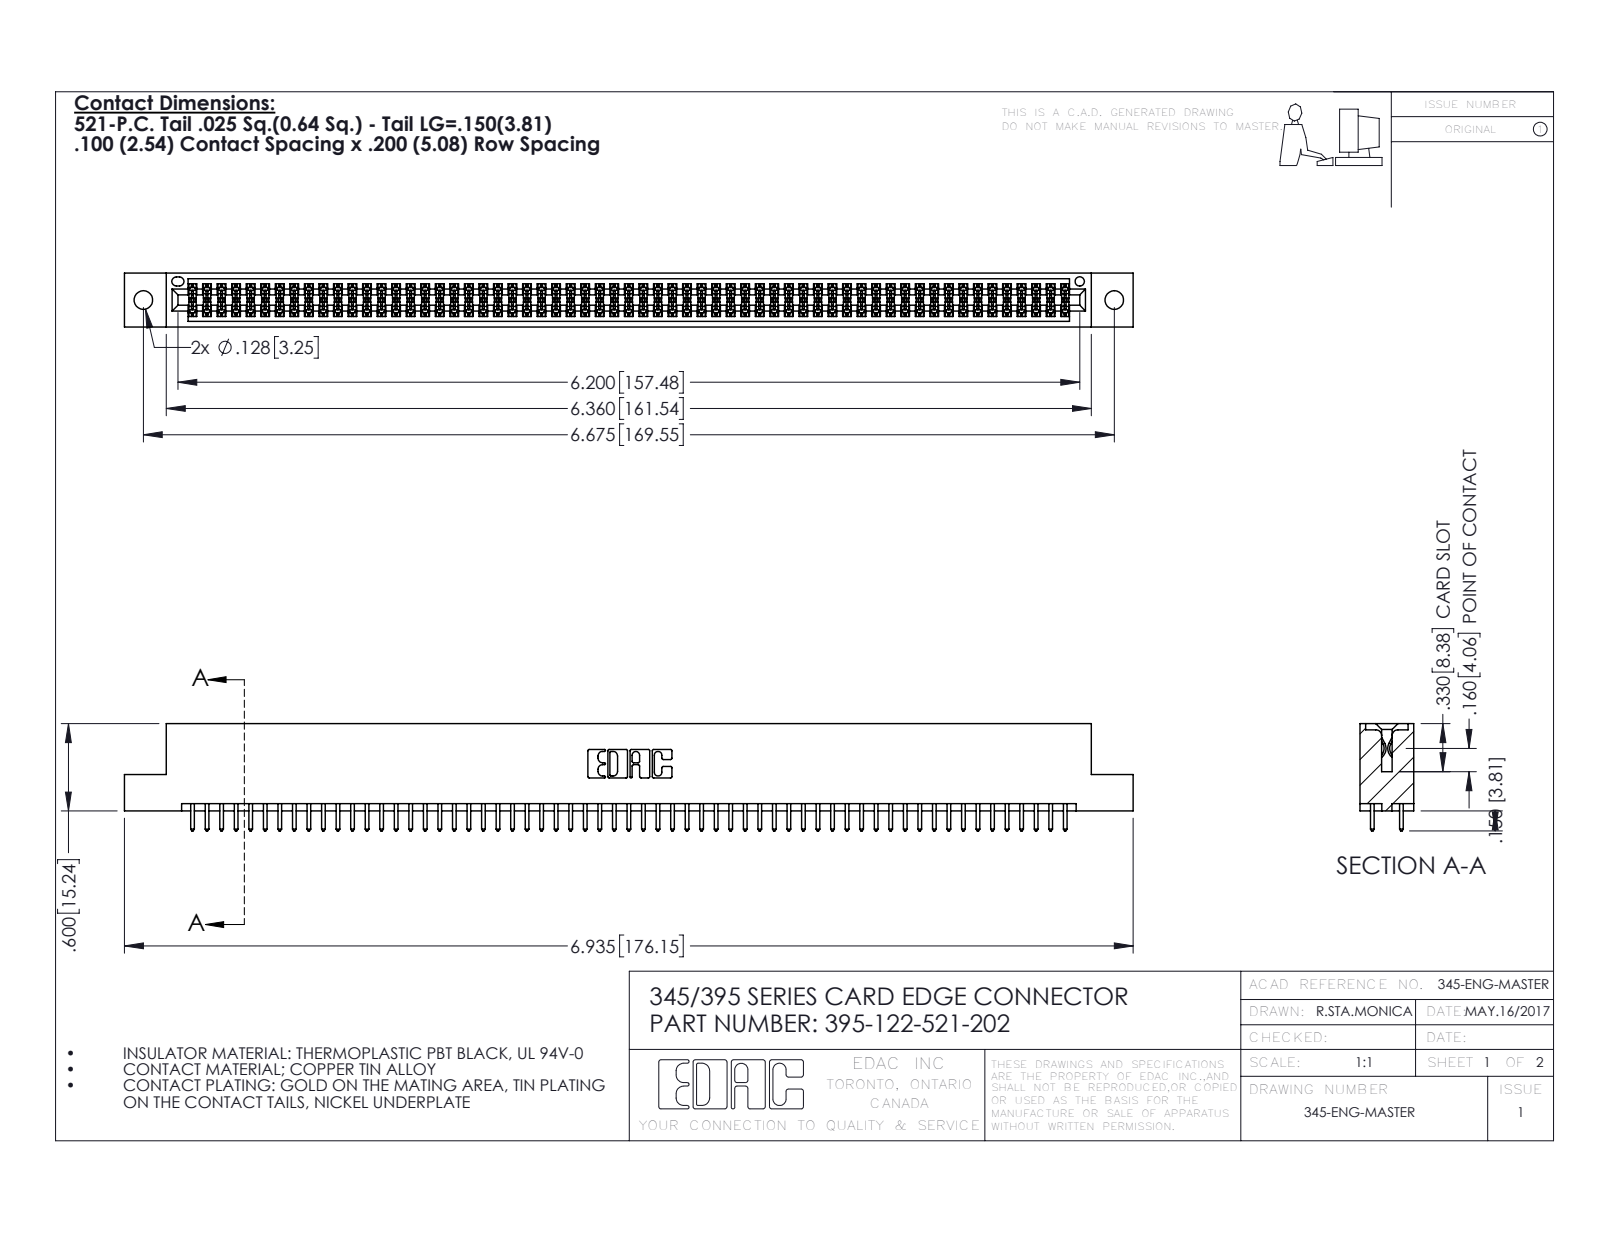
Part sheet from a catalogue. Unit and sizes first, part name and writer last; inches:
Units: inches
Overall size (bounding box): 6.935 × 0.737 × 0.37
Round holes (diameter × count): ⌀0.128 ×2, ⌀0.064 ×1
Partial cylindrical surfaces — rounded edges, fillets, slot ends (radius × count): R0.006 ×183, R0.01 ×122, R0.01 ×22, R0.007 ×6, R0.031 ×6, R0.026 ×3, R0.014 ×2, R0.019 ×2
Main face-to-face distances: 0.298, 0.072, 0.2, 0.098, 0.272, 0.025, 0.37, 0.225, 0.175, 0.149
Hole centre spacings: 0.27, 6.439, 6.675
Volume: 1.05 in³ · Surface area: 39.06 in²
Bodies: 123 solids, 6226 faces (4106 planar, 2120 cylindrical, 0 other)
Part name (STEP PRODUCT): 395-122-521-202; 345-292-001_345-293-121; 345 Part_Flush Mounting Lugs - 0.128 Dia
STEP written by: SolidWorks 2016 (CONFIG_CONTROL_DESIGN)
